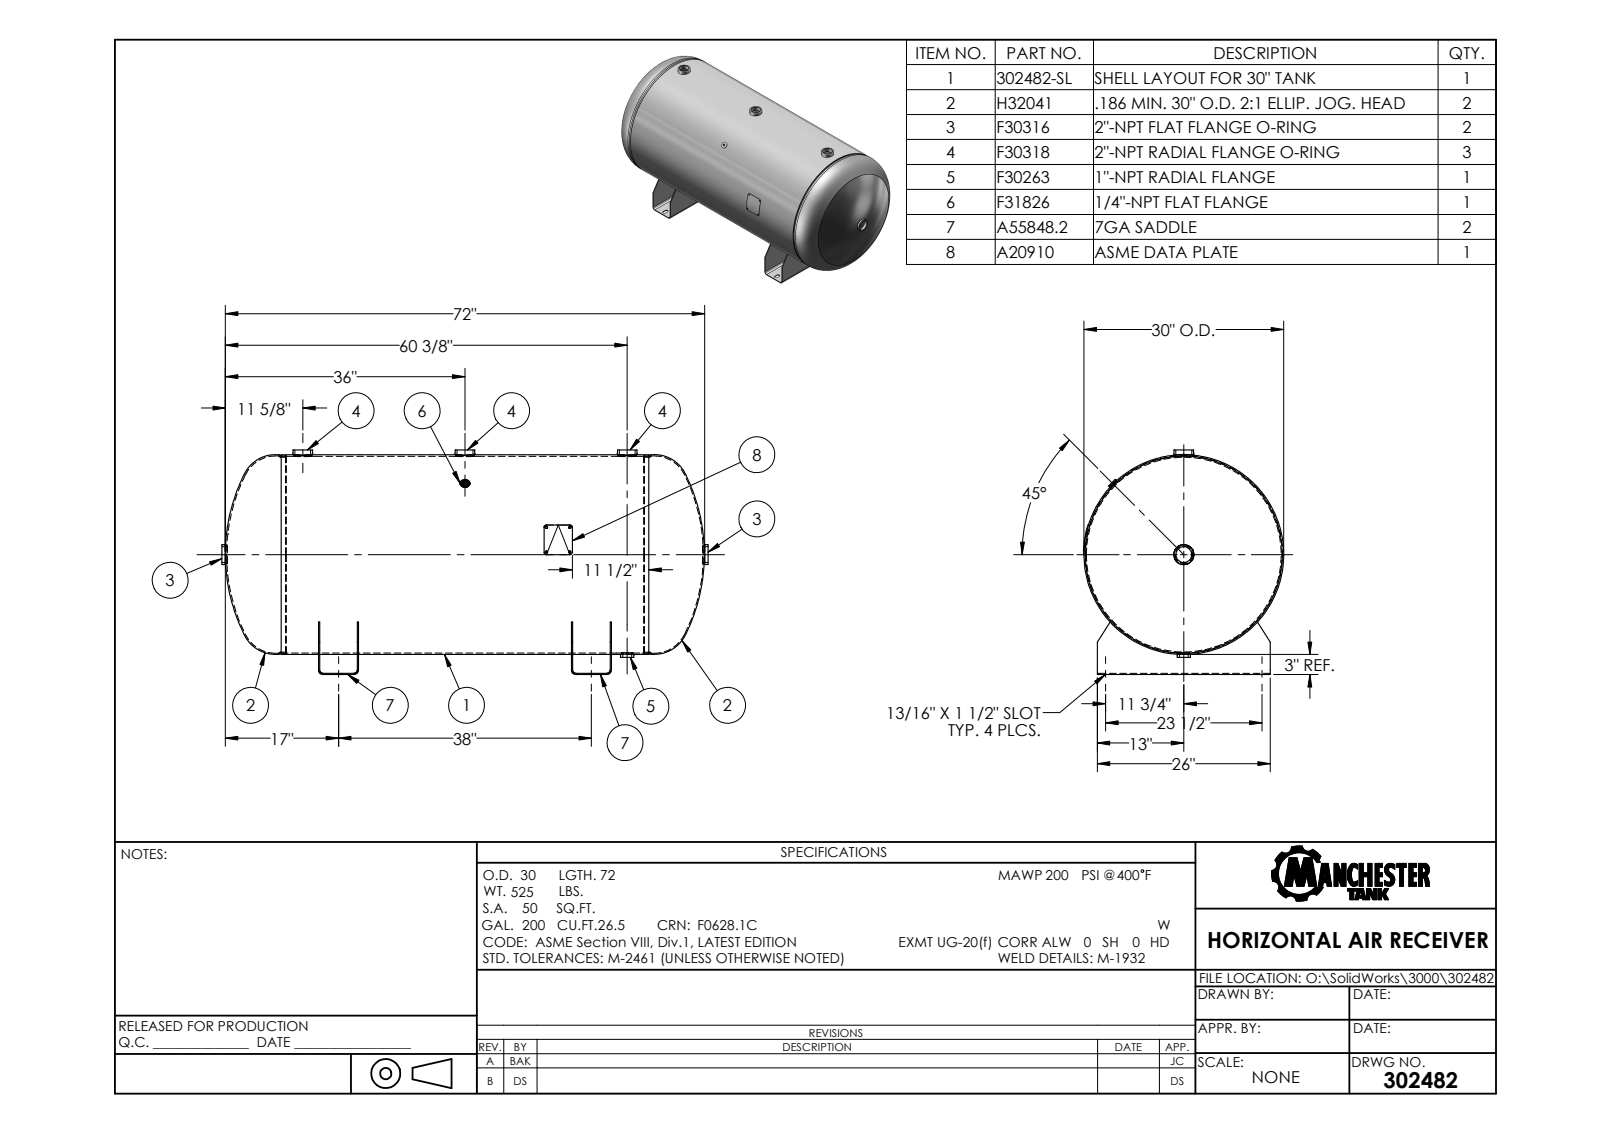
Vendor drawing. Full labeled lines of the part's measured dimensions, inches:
Part name (STEP PRODUCT): 302482
STEP written by: SolidWorks 2011 (CONFIG_CONTROL_DESIGN)
Units: inches
Bodies: 0 solids, 212 faces (63 planar, 79 cylindrical, 70 other)
Overall size (bounding box): 73.25 × 33.873 × 30.06
Round holes (diameter × count): ⌀2.375 ×4, ⌀0.54 ×1, ⌀1.315 ×1, ⌀29.546 ×1
Round bosses / shafts (diameter × count): ⌀3.625 ×2, ⌀30 ×1, ⌀29.63 ×1, ⌀3.625 ×1, ⌀3.5 ×1, ⌀2.875 ×1, ⌀1.5 ×1
Partial cylindrical surfaces — rounded edges, fillets, slot ends (radius × count): R0.406 ×8, R0.094 ×4, R0.281 ×4, R0.5 ×4, R15.031 ×1, R15.06 ×1
Main face-to-face distances: 38, 0.187, 5.813, 0.188, 32.187, 6, 38.187, 43.813, 5.625, 37.813
Hole centre spacings: 24.375, 48.75
